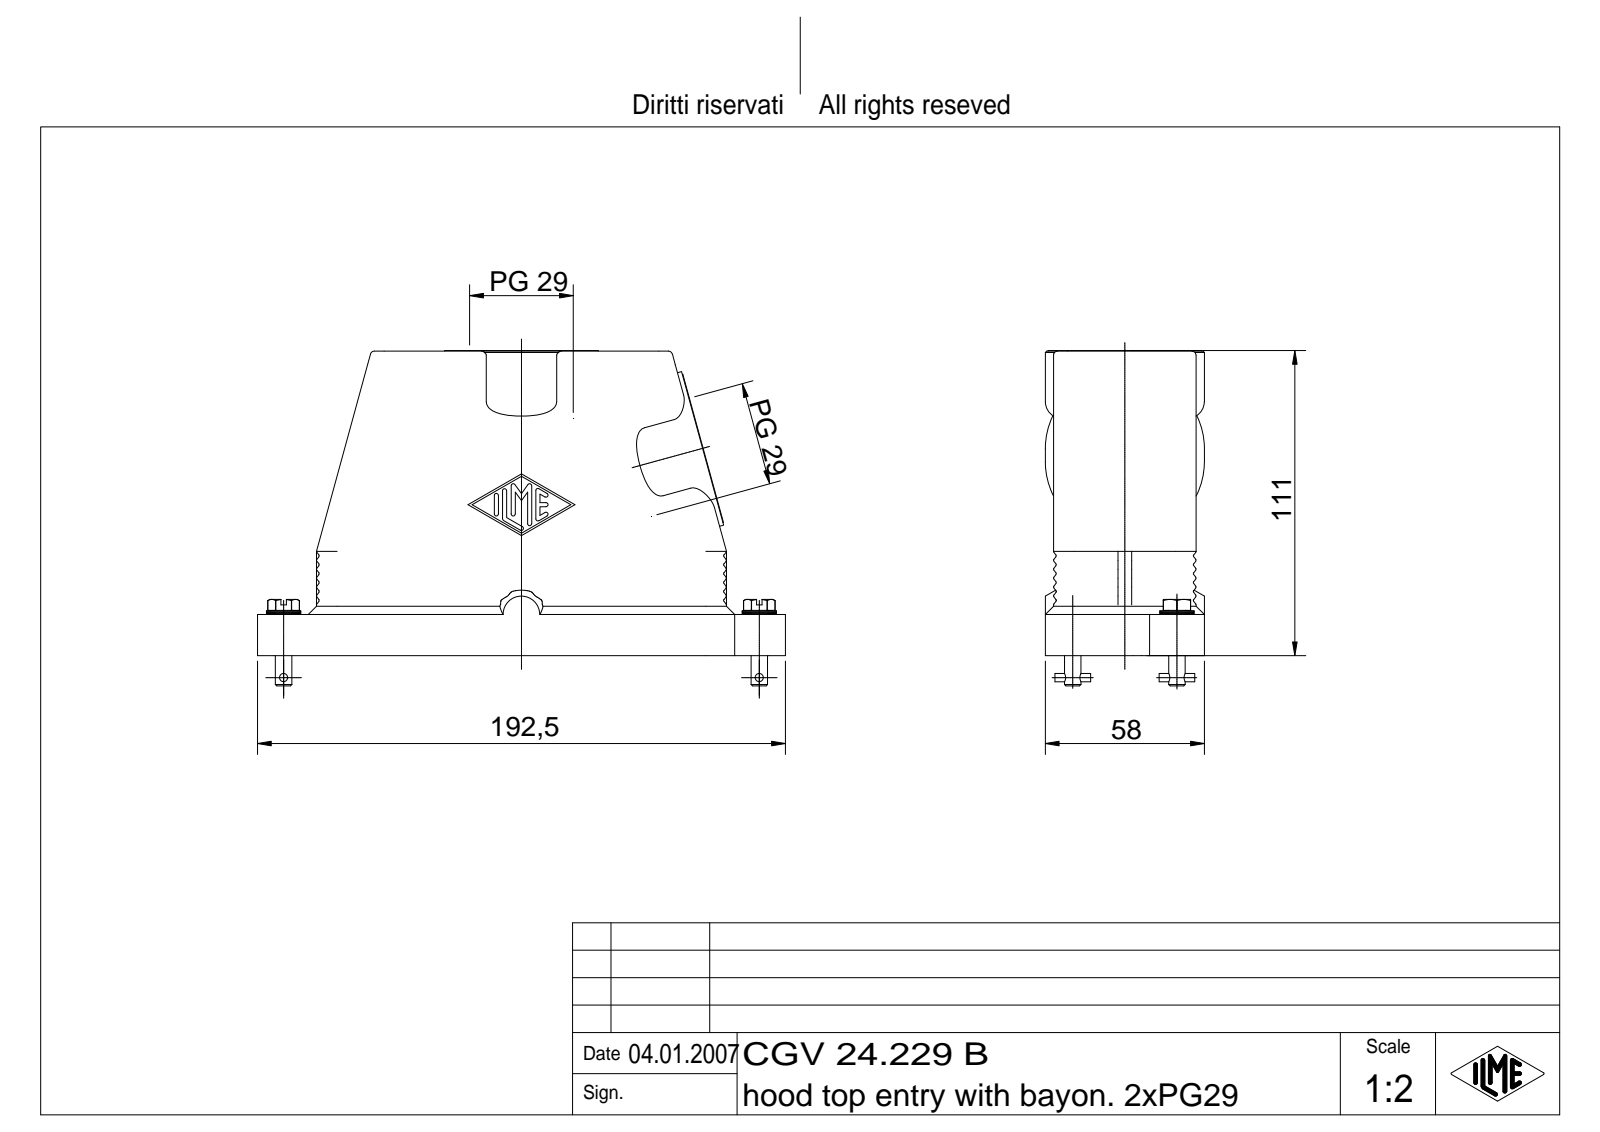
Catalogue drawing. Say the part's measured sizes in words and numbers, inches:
The part is named "CGV 24.229 B". Its 3-D file was written by "Autodesk Inventor 7 (AUTOMOTIVE_DESIGN)". It is 3 solids with 781 faces: 193 planar, 205 cylindrical and 383 other. Overall it measures 7.579 by 4.811 by 2.283 inches. Its volume is 13.89 cubic inches and its surface area 167.9 square inches. Round holes: 2 of diameter 0.097, 2 of diameter 0.126, 2 of diameter 0.26, 2 of diameter 0.591, 2 of diameter 1.397. Round bosses or shafts: 2 of diameter 2.283, 2 of diameter 2.205, 2 of diameter 0.492, 2 of diameter 0.236, 2 of diameter 0.118. Partial cylindrical surfaces (rounded edges, fillets, slot ends): 39 of radius 0.02, 14 of radius 0.03, 8 of radius 0.295, 6 of radius 0.236, 4 of radius 0.059, 4 of radius 0.118, 2 of radius 0.226, 2 of radius 0.413. The main face-to-face distances are 0.118, 2.047, 1.929, 1.811, 0.236, 2.165, 0.098, 0.02, 2.283, 0.138. The hole center spacings are 1.385, 2.115, 3.496, 5.611, 4.23, 6.993.
